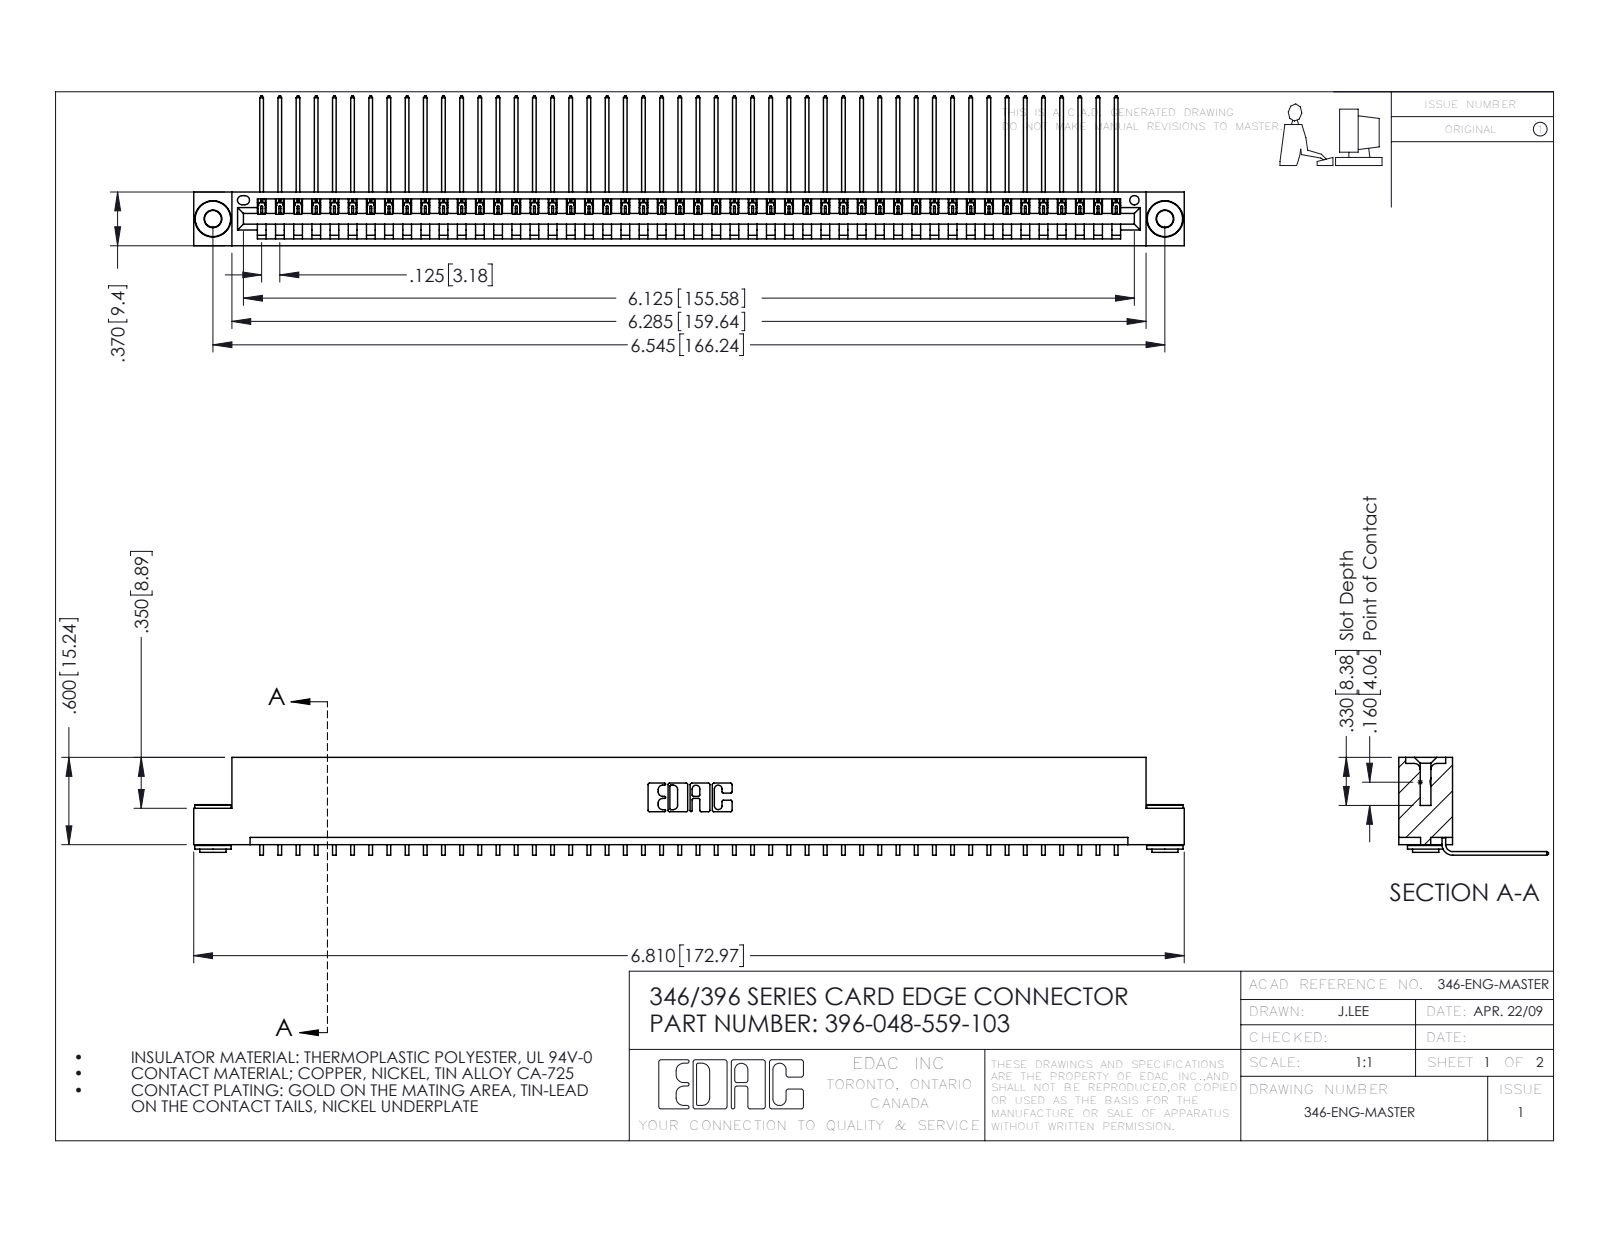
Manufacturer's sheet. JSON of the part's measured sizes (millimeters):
{"part_name": "396-048-559-103; 345-292-001_558 559 Tail - 1; 346 Part_Flush Mounting Lugs - 0.156 Dia-TH; 345-250-002_345-250-002-102", "step_written_by": "SolidWorks 2016 (CONFIG_CONTROL_DESIGN)", "units": "millimeters", "bodies": {"solids": 51, "faces": 3040, "planar": 2102, "cylindrical": 930, "other": 8}, "overall_size": [173, 26.2, 17.1], "volume_mm3": 16780, "surface_area_mm2": 22210, "round_holes": [[2.9, 2], [4, 2], [1.6, 1]], "round_bosses_or_shafts": [[6.4, 2], [4.6, 2], [3.5, 2]], "partial_cylinders_radius": [[0.2, 96], [0.3, 22], [0.2, 6], [0.8, 6], [0.7, 3], [0.8, 2], [1, 2], [0.4, 1]], "face_to_face_distances": [1.2, 8.2, 9.4, 6.4, 0.6, 1.8, 7.6, 3.8, 5.6, 2.5], "hole_center_spacings": [6.2, 160.9, 166.2]}
